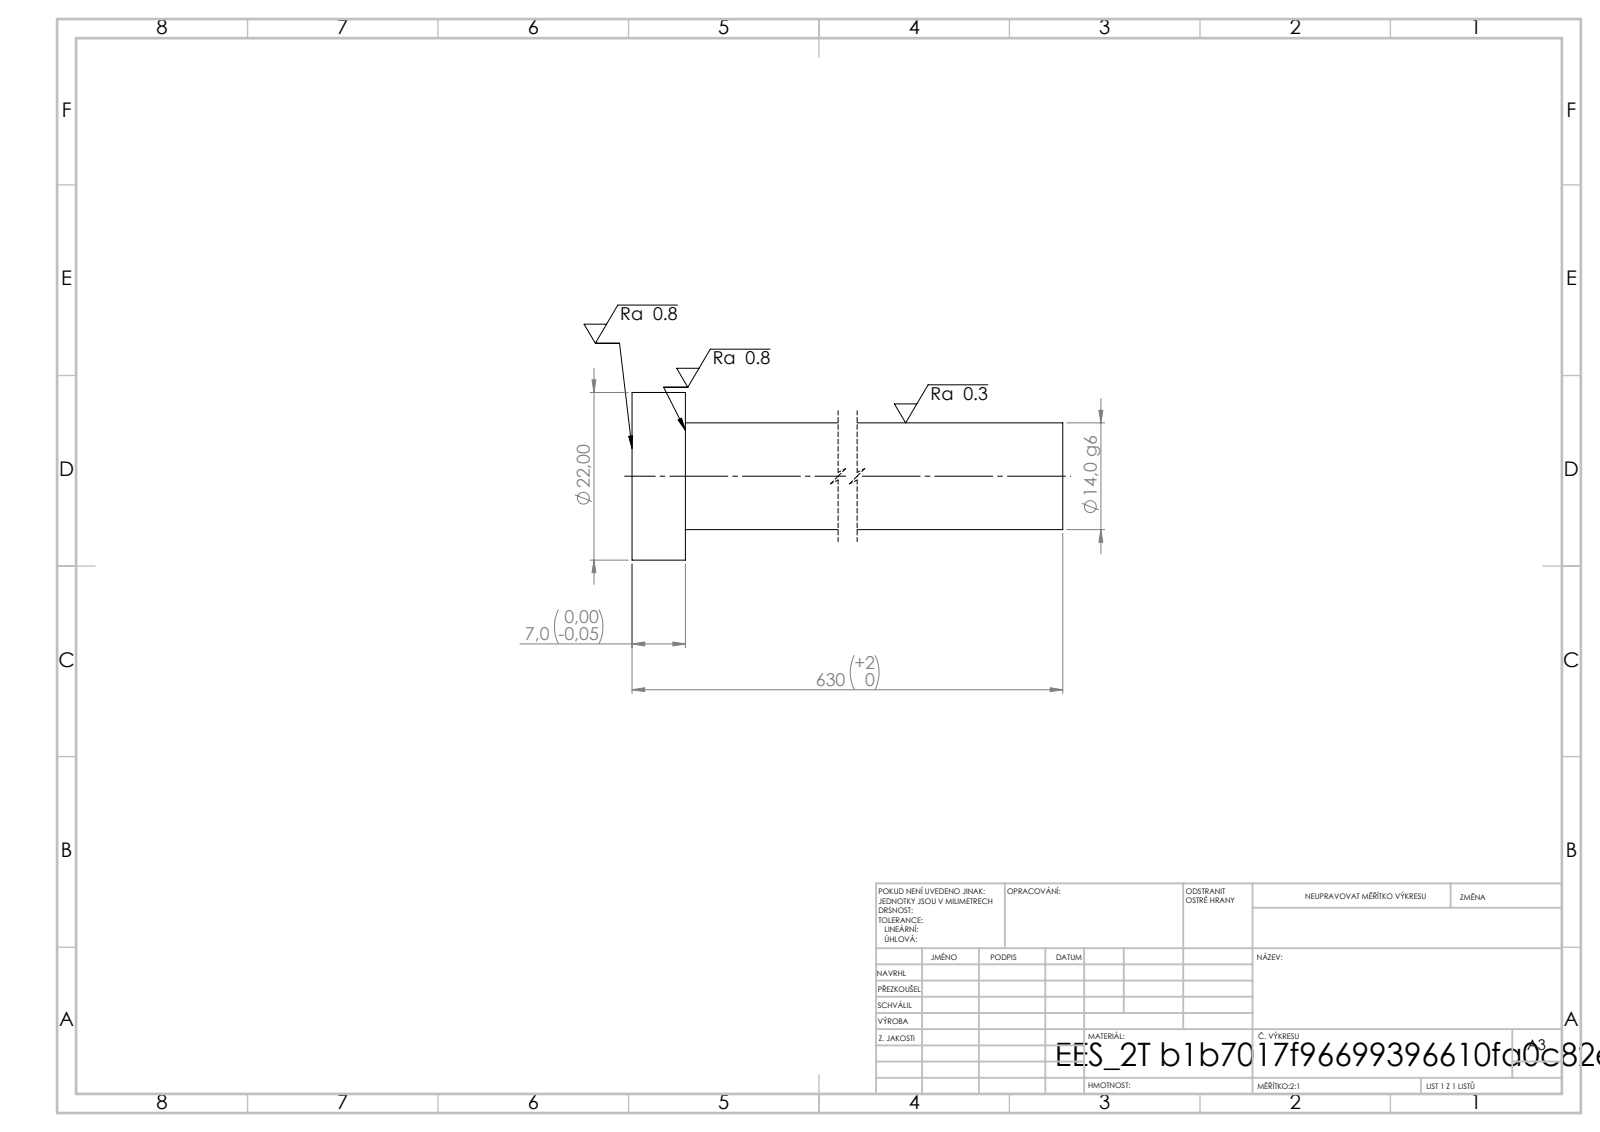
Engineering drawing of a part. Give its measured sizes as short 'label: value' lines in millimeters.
written by: SolidWorks 2019 (CONFIG_CONTROL_DESIGN)
unit: mm
bodies: 1 solid, 7 faces (3 planar, 4 cylindrical, 0 other)
size: 630 × 22 × 22
volume: 98 564 mm³; area: 28 645 mm²
bosses: 1× ⌀22, 1× ⌀14
face distances: 7, 630, 623
